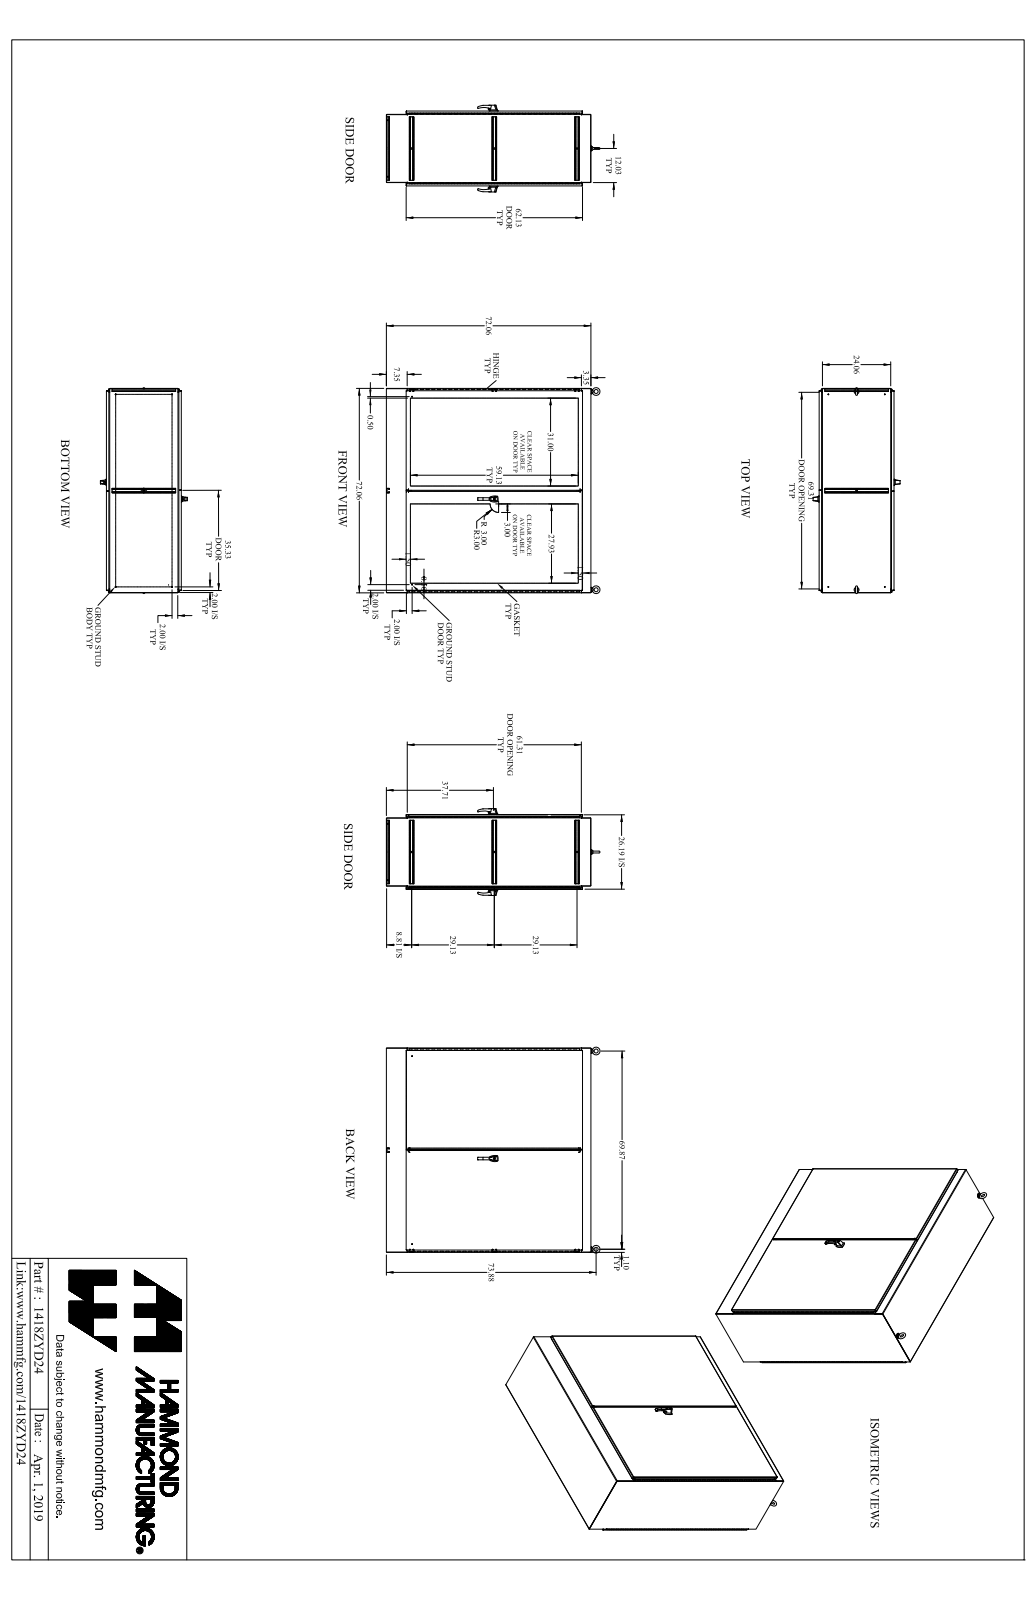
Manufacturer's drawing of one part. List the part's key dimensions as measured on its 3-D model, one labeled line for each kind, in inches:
Part name (STEP PRODUCT): 1418ZYD24_Default
STEP written by: SolidWorks 2019 (CONFIG_CONTROL_DESIGN)
Units: inches
Bodies: 110 solids, 4540 faces (2062 planar, 2212 cylindrical, 266 other)
Overall size (bounding box): 75.713 × 73.119 × 30.614
Volume: 2 078 in³ · Surface area: 42 931 in²
Round holes (diameter × count): ⌀0.304 ×40, ⌀0.11 ×4, ⌀0.25 ×4, ⌀0.257 ×4, ⌀0.28 ×4, ⌀0.281 ×4, ⌀0.313 ×4, ⌀0.39 ×4, ⌀0.413 ×4, ⌀0.5 ×4, ⌀0.173 ×2, ⌀0.233 ×2
Round bosses / shafts (diameter × count): ⌀0.281 ×12, ⌀0.25 ×8, ⌀1 ×4, ⌀0.75 ×4, ⌀0.63 ×4, ⌀0.625 ×4, ⌀0.44 ×4, ⌀0.37 ×4
Partial cylindrical surfaces — rounded edges, fillets, slot ends (radius × count): R0.043 ×54, R0.138 ×48, R0.125 ×44, R0.048 ×40, R0.143 ×40, R0.018 ×32, R0.05 ×16, R0.06 ×16
Main face-to-face distances: 0.095, 0.095, 26.289, 71.965, 26.194, 26.384, 71.87, 72.06, 1.162, 25.222
Hole centre spacings: 6, 12, 18, 70.584, 24, 71.345, 30, 72.596
